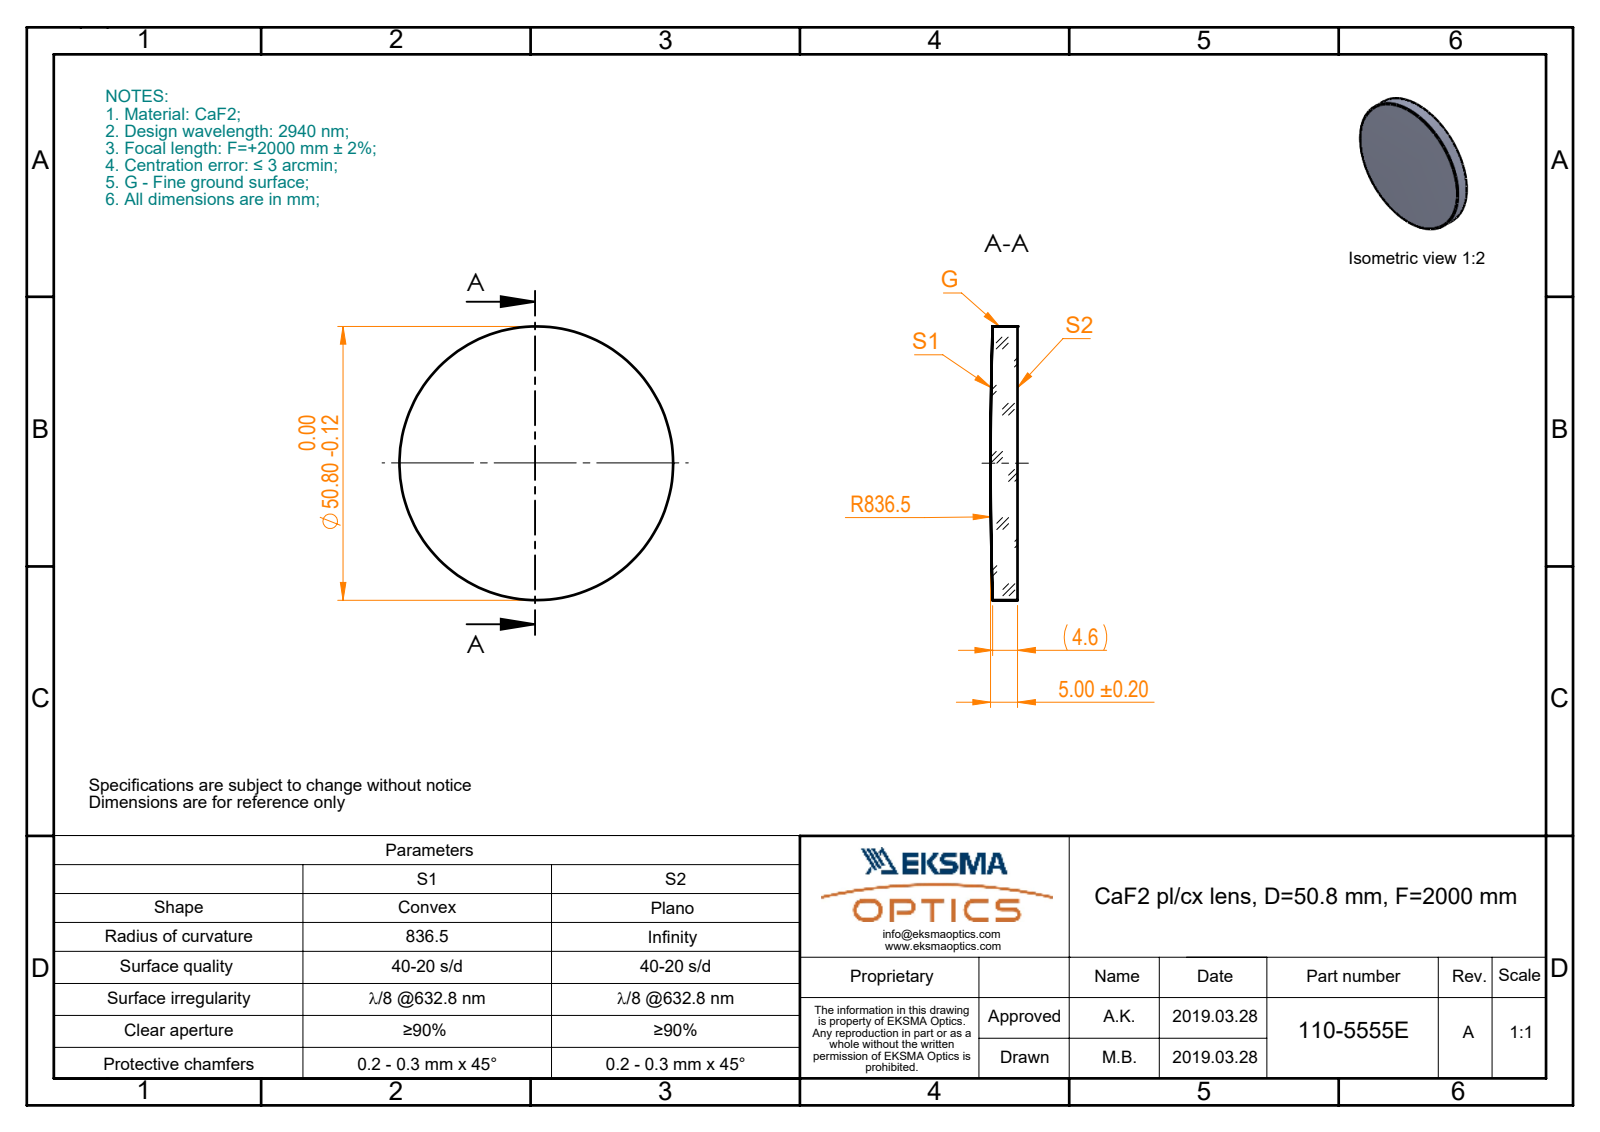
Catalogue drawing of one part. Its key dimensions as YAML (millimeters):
part_name: "110-5555E CaF2 pl-cx 50.8 F2000"
step_written_by: "SolidWorks 2017 (CONFIG_CONTROL_DESIGN)"
units: millimeters
bodies: {solids: 1, faces: 5, planar: 1, cylindrical: 2, other: 2}
overall_size: [50.8, 50.8, 5]
volume: 9743
surface_area: 4791
round_bosses_or_shafts:
  - {diameter: 50.8, count: 1}
